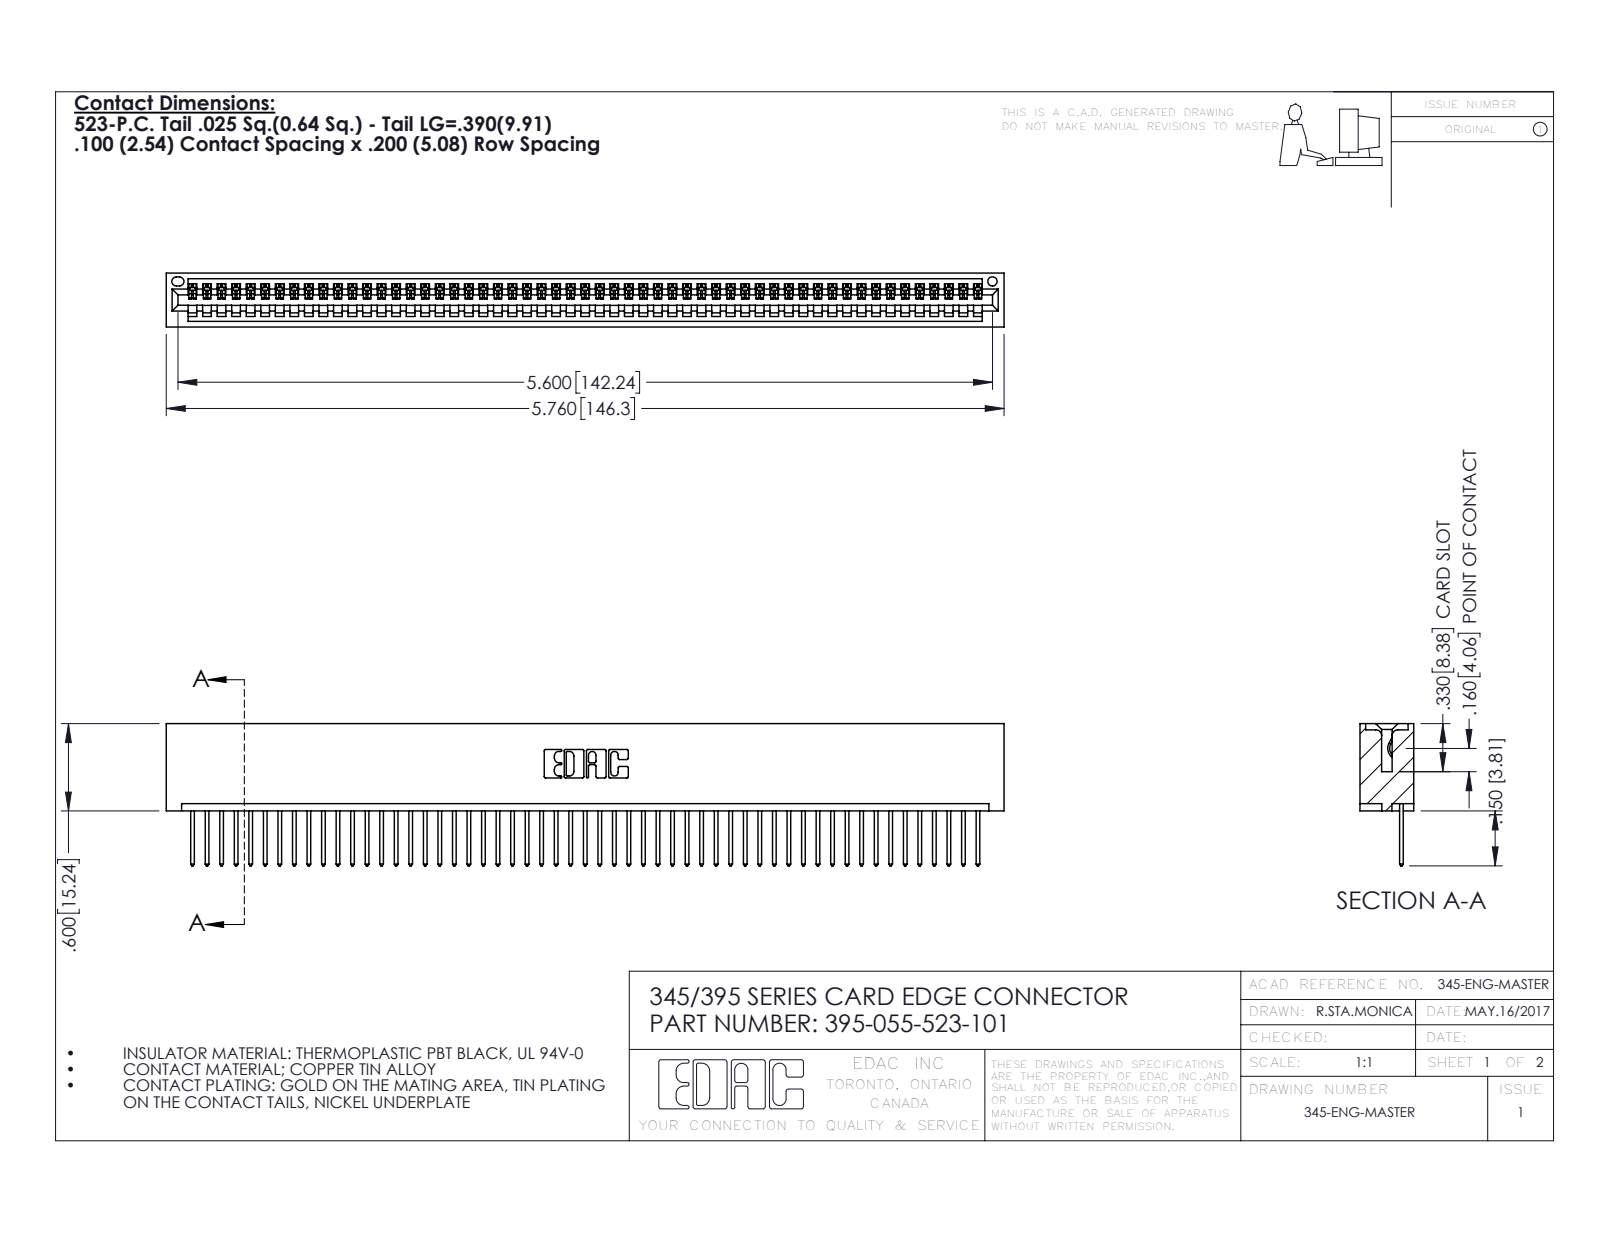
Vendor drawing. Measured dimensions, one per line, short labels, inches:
name: 345 Part_No Mounting Lugs; 395-055-523-101; 345-292-001_345-293-123
written by: SolidWorks 2016 (CONFIG_CONTROL_DESIGN)
unit: in
bodies: 56 solids, 3308 faces (2276 planar, 1032 cylindrical, 0 other)
size: 5.76 × 0.977 × 0.37
volume: 0.889 in³; area: 30.66 in²
holes: 1× ⌀0.064
rounds: 110× R0.006, 110× R0.01, 22× R0.01, 6× R0.007, 6× R0.031, 3× R0.026, 2× R0.031, 2× R0.04
face distances: 0.298, 0.072, 0.37, 0.2, 0.098, 0.272, 0.025, 0.225, 0.149, 0.072
